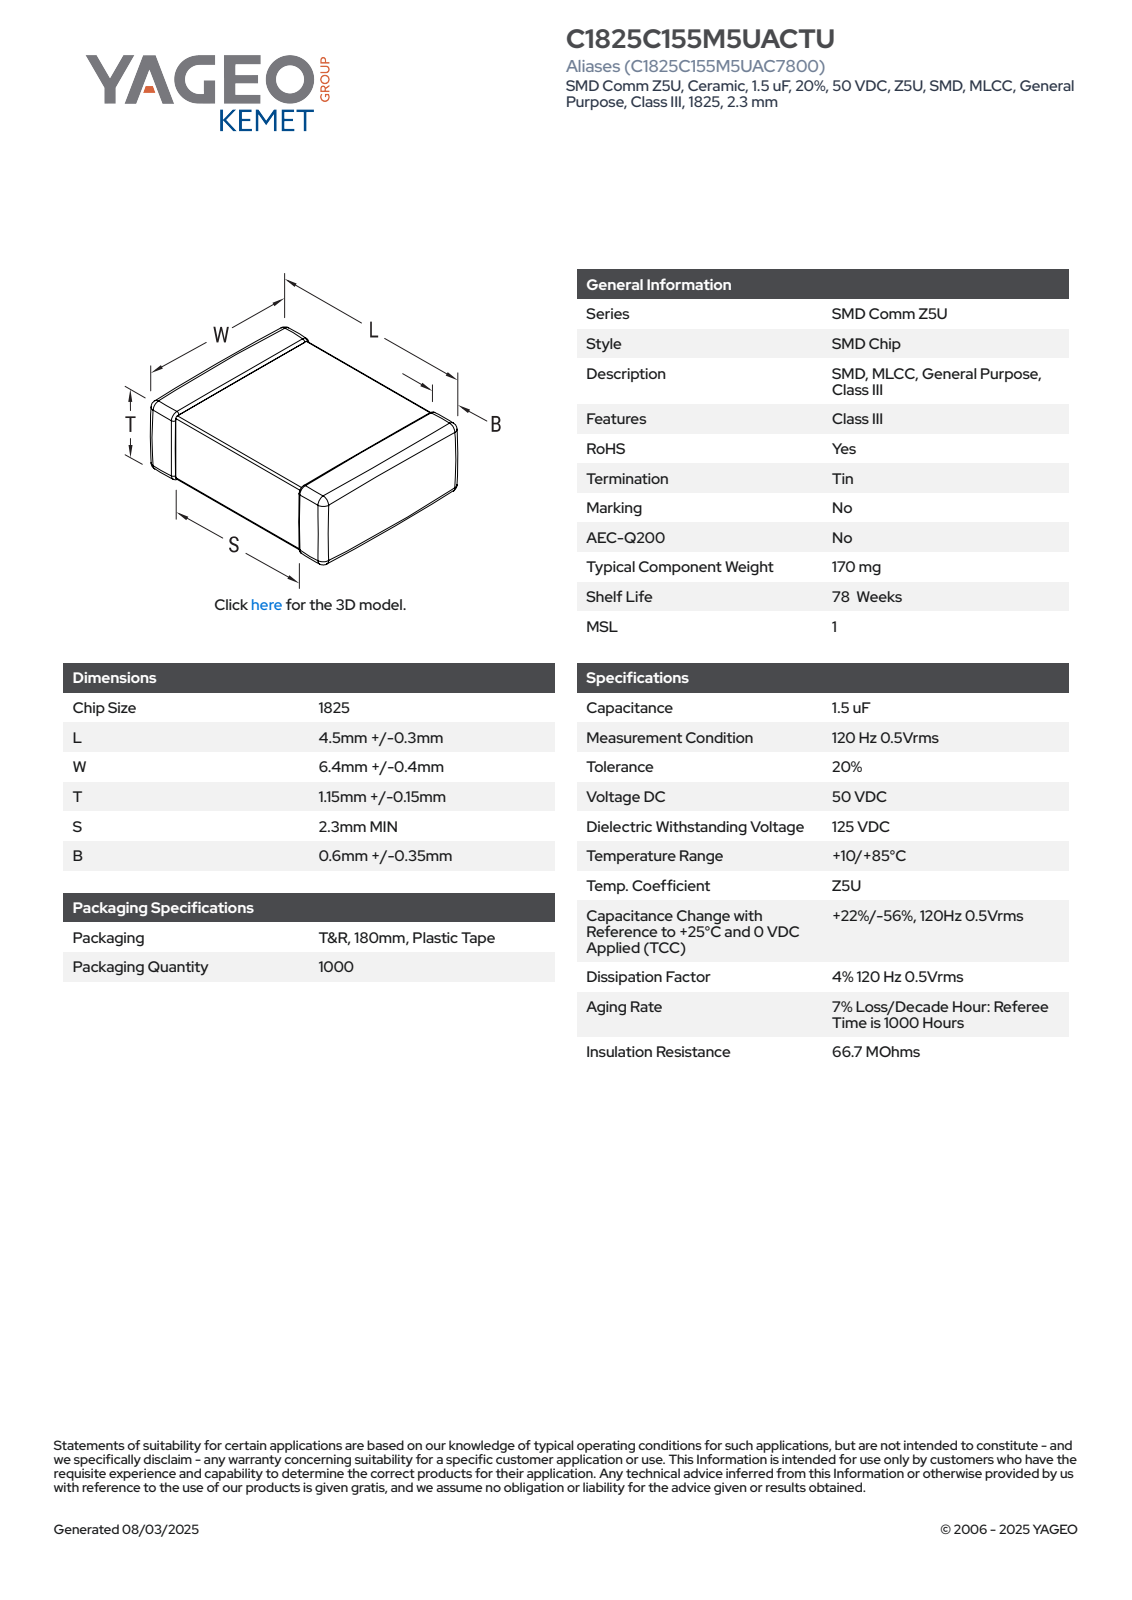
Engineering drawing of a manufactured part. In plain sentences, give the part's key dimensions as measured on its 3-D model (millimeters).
The part is named "CCS_CCSTDNOS_1825_L4.8W6.8T1.3B0.95". Its 3-D file was written by "SolidWorks 2014 (AUTOMOTIVE_DESIGN)". It is 4 solids with 121 faces: 71 planar, 34 cylindrical and 16 other. Overall it measures 6.8 by 4.8 by 1.3 millimeters. Its volume is 36 cubic millimeters and its surface area 92 square millimeters. Partial cylindrical surfaces (rounded edges, fillets, slot ends): 24 of radius 0.14. The main face-to-face distances are 1.02, 1.16, 1.3, 4.8, 6.66, 6.52, 6.8, 0.34, 3.56, 3.42.
